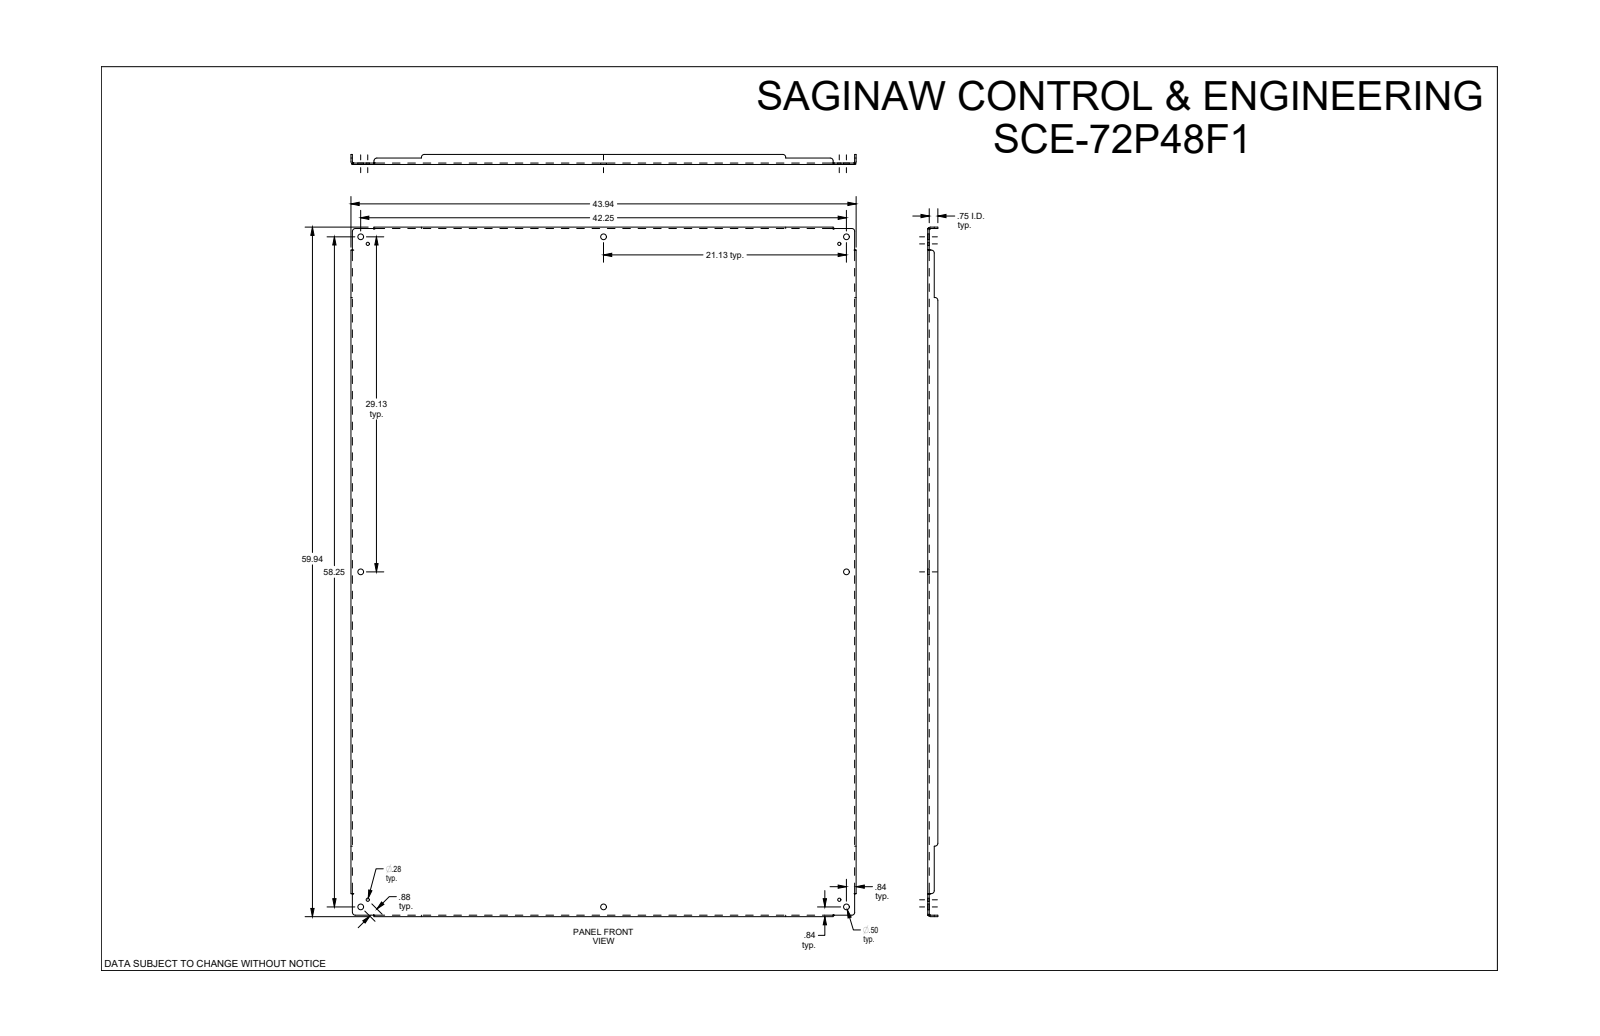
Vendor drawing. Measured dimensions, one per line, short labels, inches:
name: SCE-72P48F1
written by: SolidWorks 2019 (CONFIG_CONTROL_DESIGN)
unit: in
bodies: 1 solid, 110 faces (46 planar, 40 cylindrical, 24 other)
size: 59.938 × 43.938 × 0.875
volume: 343.6 in³; area: 5 526 in²
holes: 8× ⌀0.5, 4× ⌀0.281
rounds: 12× R0.25, 4× R0.112, 4× R0.237
face distances: 0.125, 0.125, 43.813, 59.813, 43.687, 43.938, 59.687, 59.938, 0.75, 0.875
hole spacings: 0.875, 20.516, 21.125, 28.513, 29.125, 35.979, 41.636, 50.456
